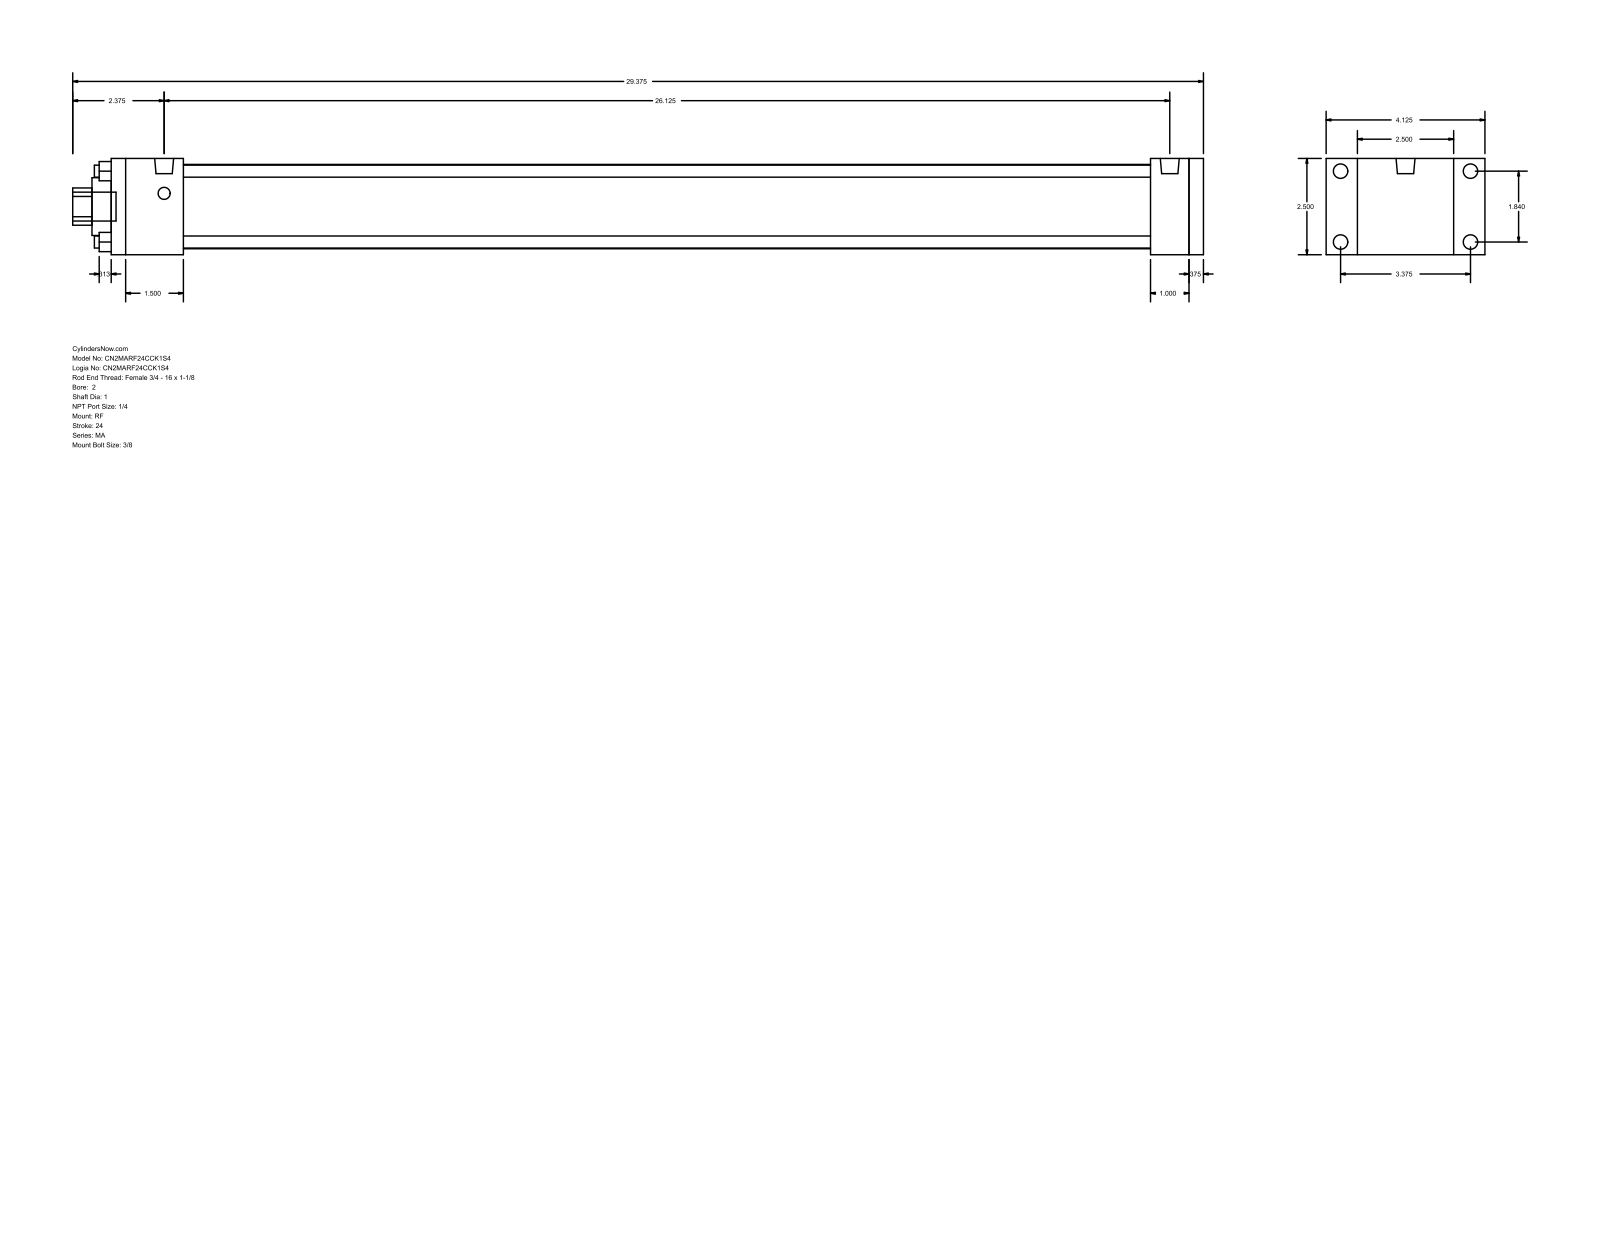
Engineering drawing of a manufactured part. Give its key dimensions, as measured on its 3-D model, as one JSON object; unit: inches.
{"part_name": "MA_RF__0200_1", "step_written_by": "GSSL Pune (CONFIG_CONTROL_DESIGN)", "units": "inches", "bodies": {"solids": 0, "faces": 92, "planar": 64, "cylindrical": 28, "other": 0}, "overall_size": [29.375, 4.125, 2.5], "round_holes": [[0.313, 4], [1, 1], [1.5, 1], [2.19, 1]], "round_bosses_or_shafts": [[0.375, 4], [0.313, 4], [0.492, 2], [0.75, 1]], "partial_cylinders_radius": [[0.484, 1]], "face_to_face_distances": [2.5, 28, 0.375, 28.375, 1, 0.813, 0.5, 1.875, 26.125, 26.5], "hole_center_spacings": [1.301, 1.84, 2.602]}
